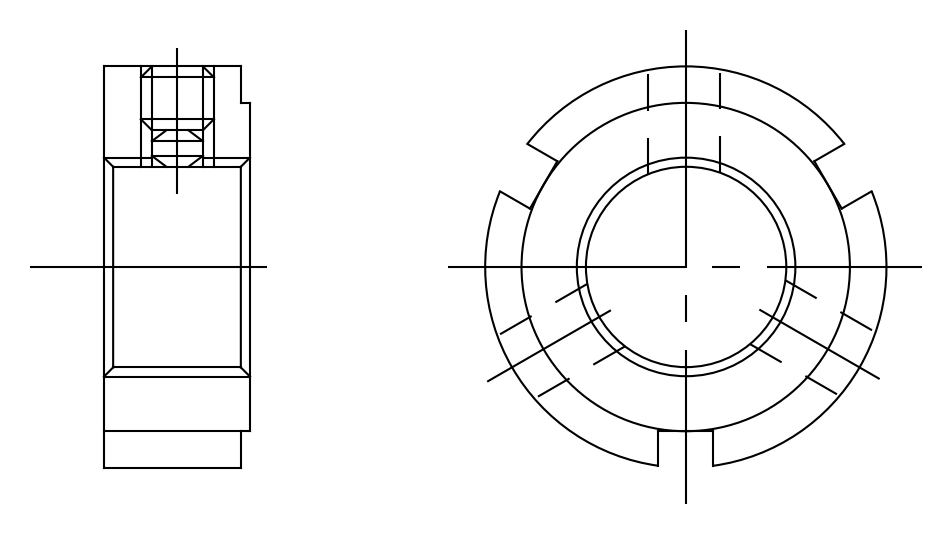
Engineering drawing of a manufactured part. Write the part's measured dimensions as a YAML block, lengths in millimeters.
part_name: "FKD ZMT 12"
step_written_by: "Autodesk Inventor 2011 (AUTOMOTIVE_DESIGN)"
units: millimeters
bodies: {solids: 1, faces: 22, planar: 14, cylindrical: 8, other: 0}
overall_size: [22, 21.9, 8]
volume: 1816
surface_area: 1537
round_holes:
  - {diameter: 3.24, count: 3}
  - {diameter: 12, count: 1}
round_bosses_or_shafts:
  - {diameter: 22, count: 1}
  - {diameter: 18, count: 1}
face_to_face_distances: [8, 0.5, 7.5, 3]
